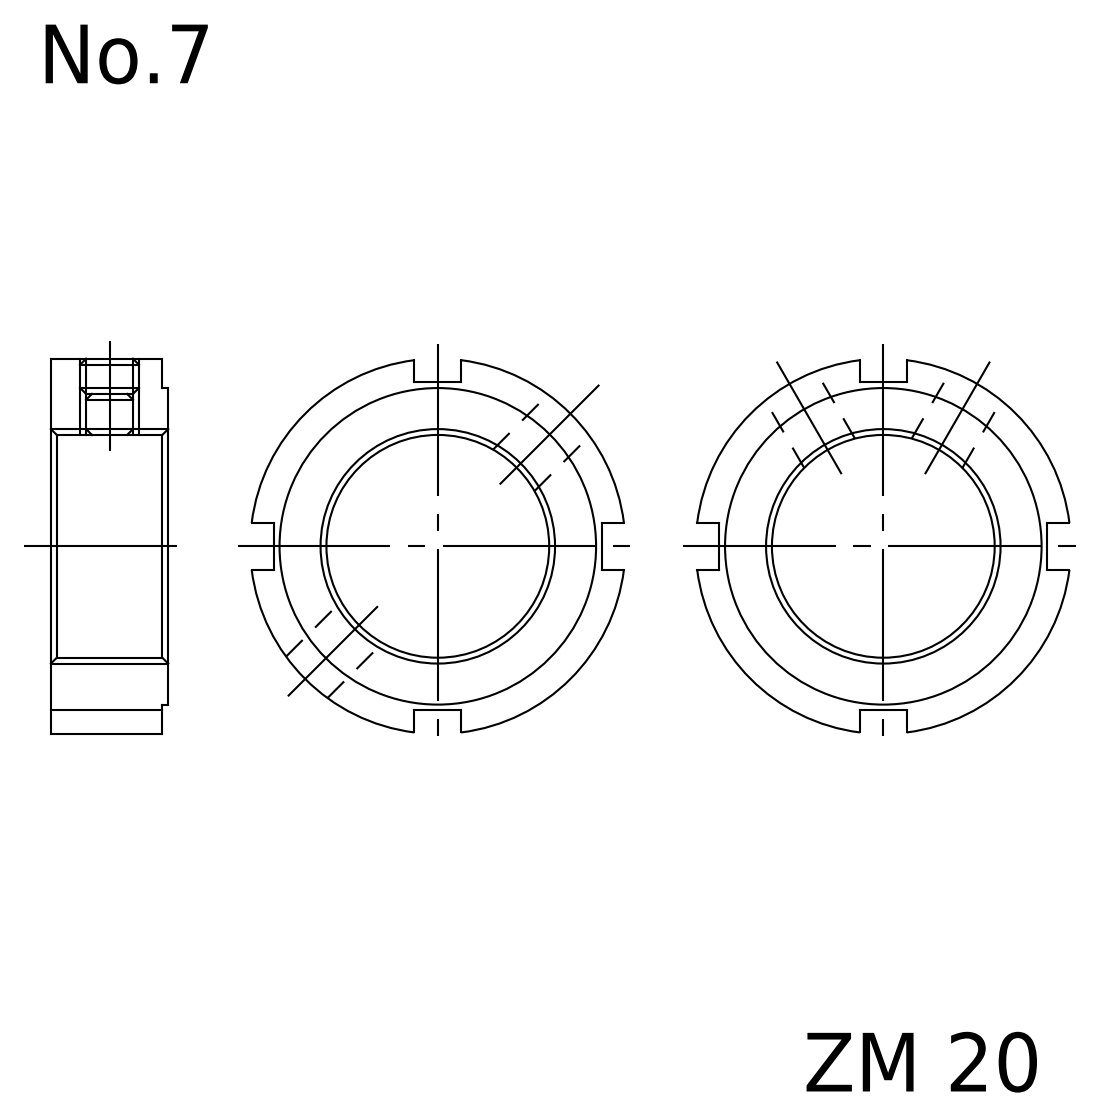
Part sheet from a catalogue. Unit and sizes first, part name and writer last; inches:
Units: inches
Overall size (bounding box): 1.25 × 1.25 × 0.394
Round holes (diameter × count): ⌀0.163 ×2, ⌀0.787 ×1
Round bosses / shafts (diameter × count): ⌀1.26 ×1, ⌀1.063 ×1
Main face-to-face distances: 0.394, 0.02, 0.374, 0.472, 0.63, 1.102, 0.157
Volume: 0.264 in³ · Surface area: 4.321 in²
Bodies: 1 solid, 23 faces (15 planar, 8 cylindrical, 0 other)
Part name (STEP PRODUCT): FKD ZM 20
STEP written by: Autodesk Inventor 2011 (AUTOMOTIVE_DESIGN)
